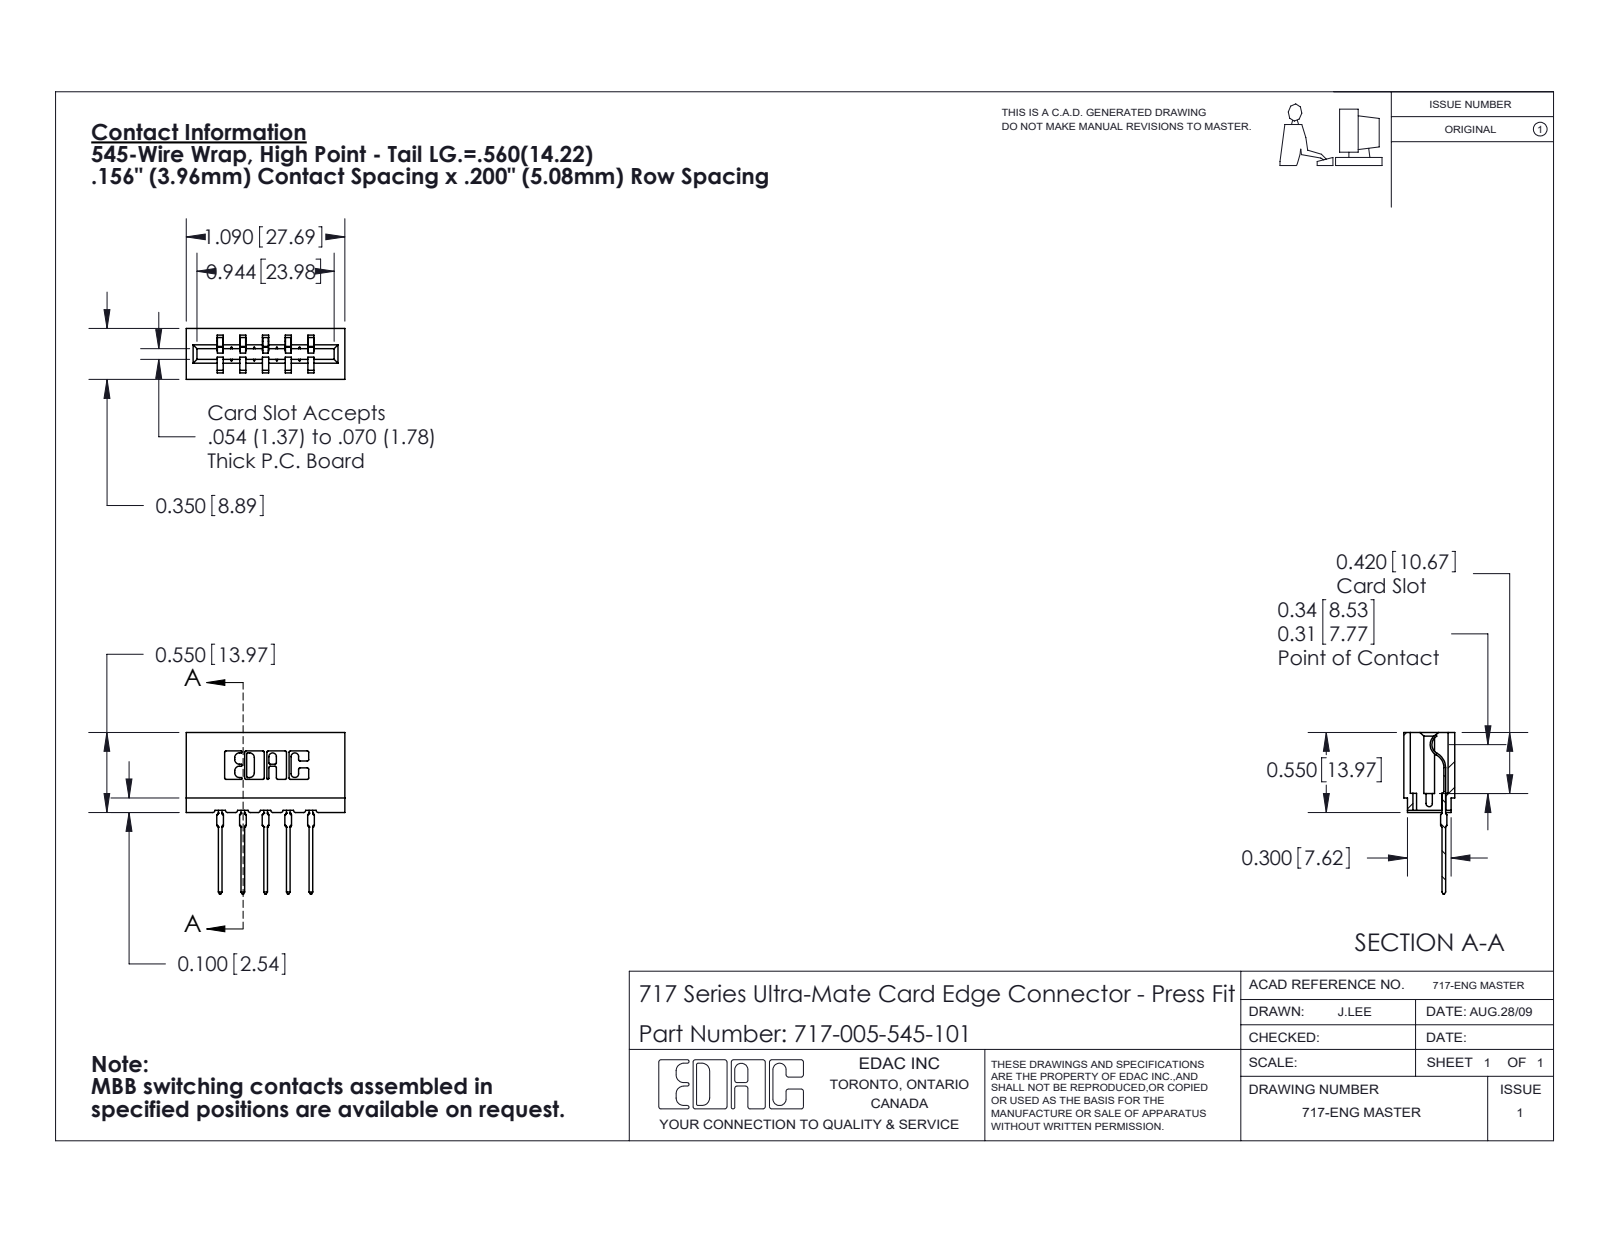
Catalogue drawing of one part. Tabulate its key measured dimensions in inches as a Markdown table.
| quantity | value |
| --- | --- |
| part name | 745-292-001_545; 717 Part_Insulator Option - 06; 717-005-545-101 |
| STEP written by | SolidWorks 2020 (CONFIG_CONTROL_DESIGN) |
| units | inches |
| bodies | 6 solids, 659 faces (394 planar, 135 cylindrical, 130 other) |
| overall size | 1.109 × 1.09 × 0.35 |
| volume | 0.154 in³ |
| surface area | 4.985 in² |
| partial cylindrical surfaces (radius × count) | 0.01 × 22, 0.015 × 10, 0.021 × 10, 0.007 × 6, 0.031 × 6, 0.005 × 4, 0.011 × 4, 0.026 × 3 |
| main face-to-face distances | 0.212, 0.156, 0.138, 0.35, 0.198, 0.042, 0.312, 0.312, 0.468, 0.074 |
